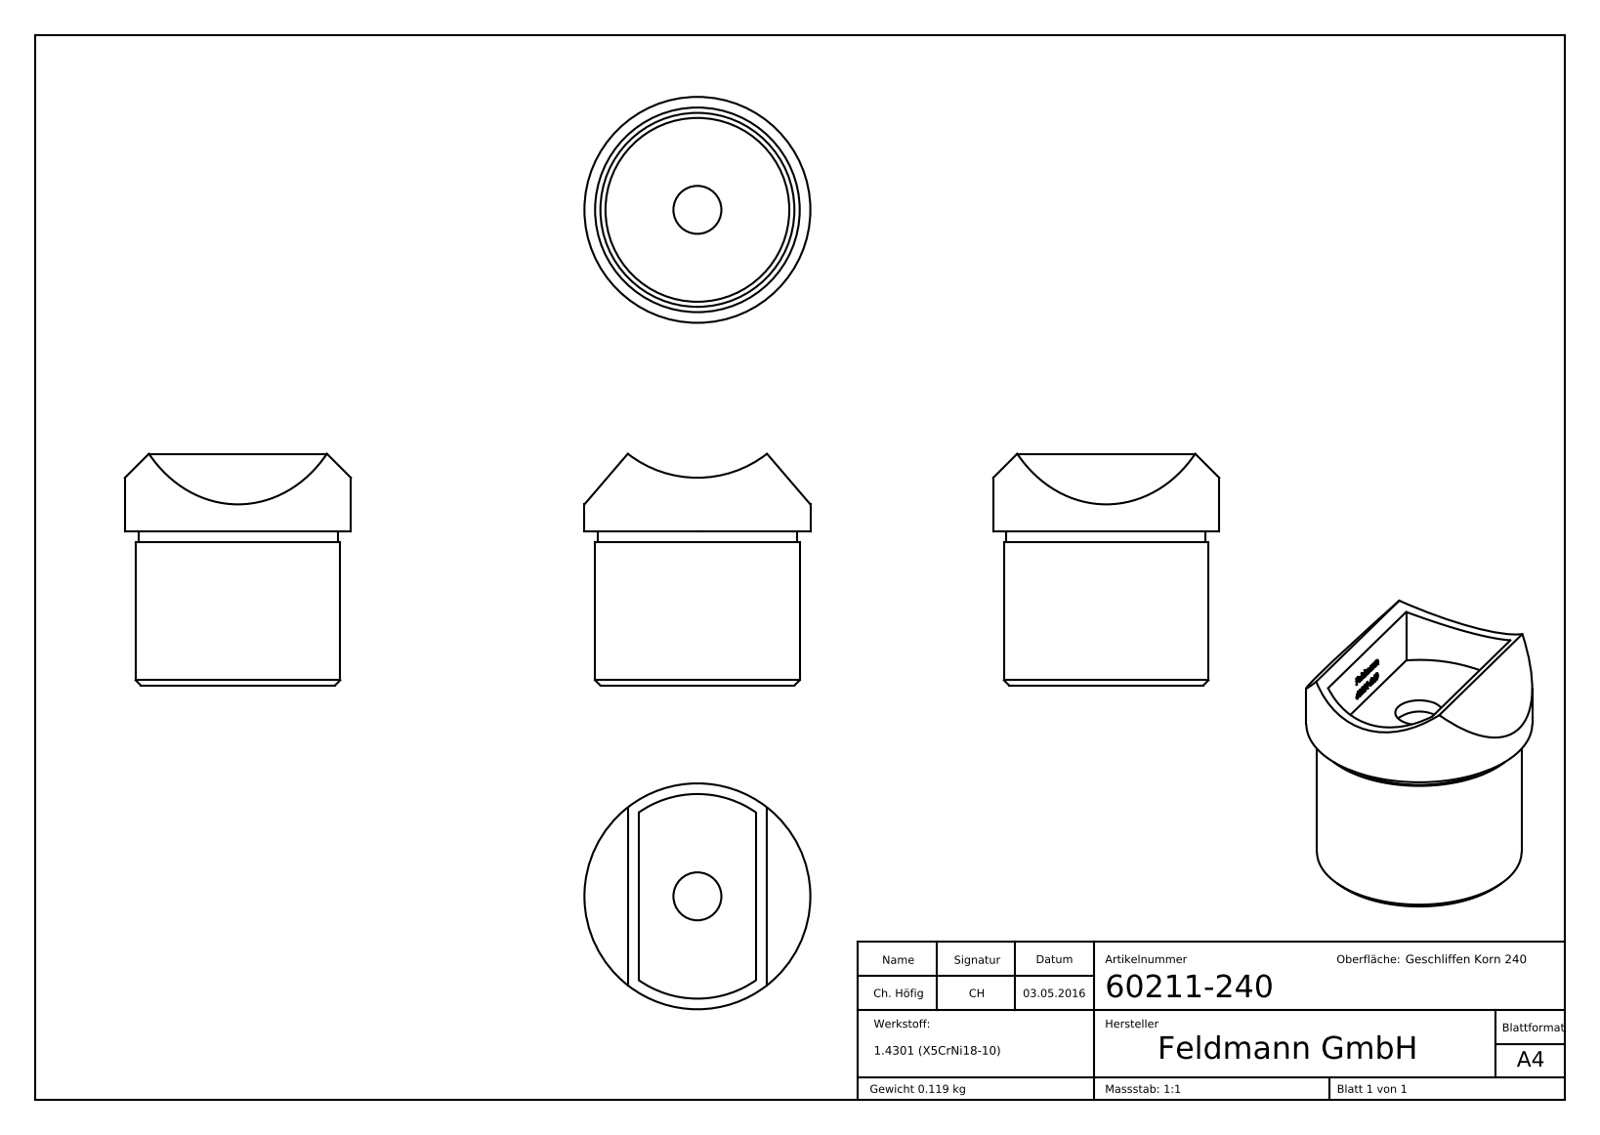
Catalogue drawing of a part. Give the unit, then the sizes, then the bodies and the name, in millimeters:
Units: millimetres
Overall size (bounding box): 43.5 × 42.4 × 42.4
Round holes (diameter × count): ⌀9 ×1, ⌀34.5 ×1, ⌀38.4 ×1
Round bosses / shafts (diameter × count): ⌀42.4 ×1, ⌀37.4 ×1
Partial cylindrical surfaces — rounded edges, fillets, slot ends (radius × count): R21.2 ×1
Main face-to-face distances: 2.5, 22.12, 29, 31.5, 4.5, 27, 2, 22.22, 3.21, 4.6
Volume: 15 122 mm³ · Surface area: 12 051 mm²
Bodies: 1 solid, 233 faces (131 planar, 13 cylindrical, 89 other)
Part name (STEP PRODUCT): 60211-240
STEP written by: SolidWorks 2015 (CONFIG_CONTROL_DESIGN)
